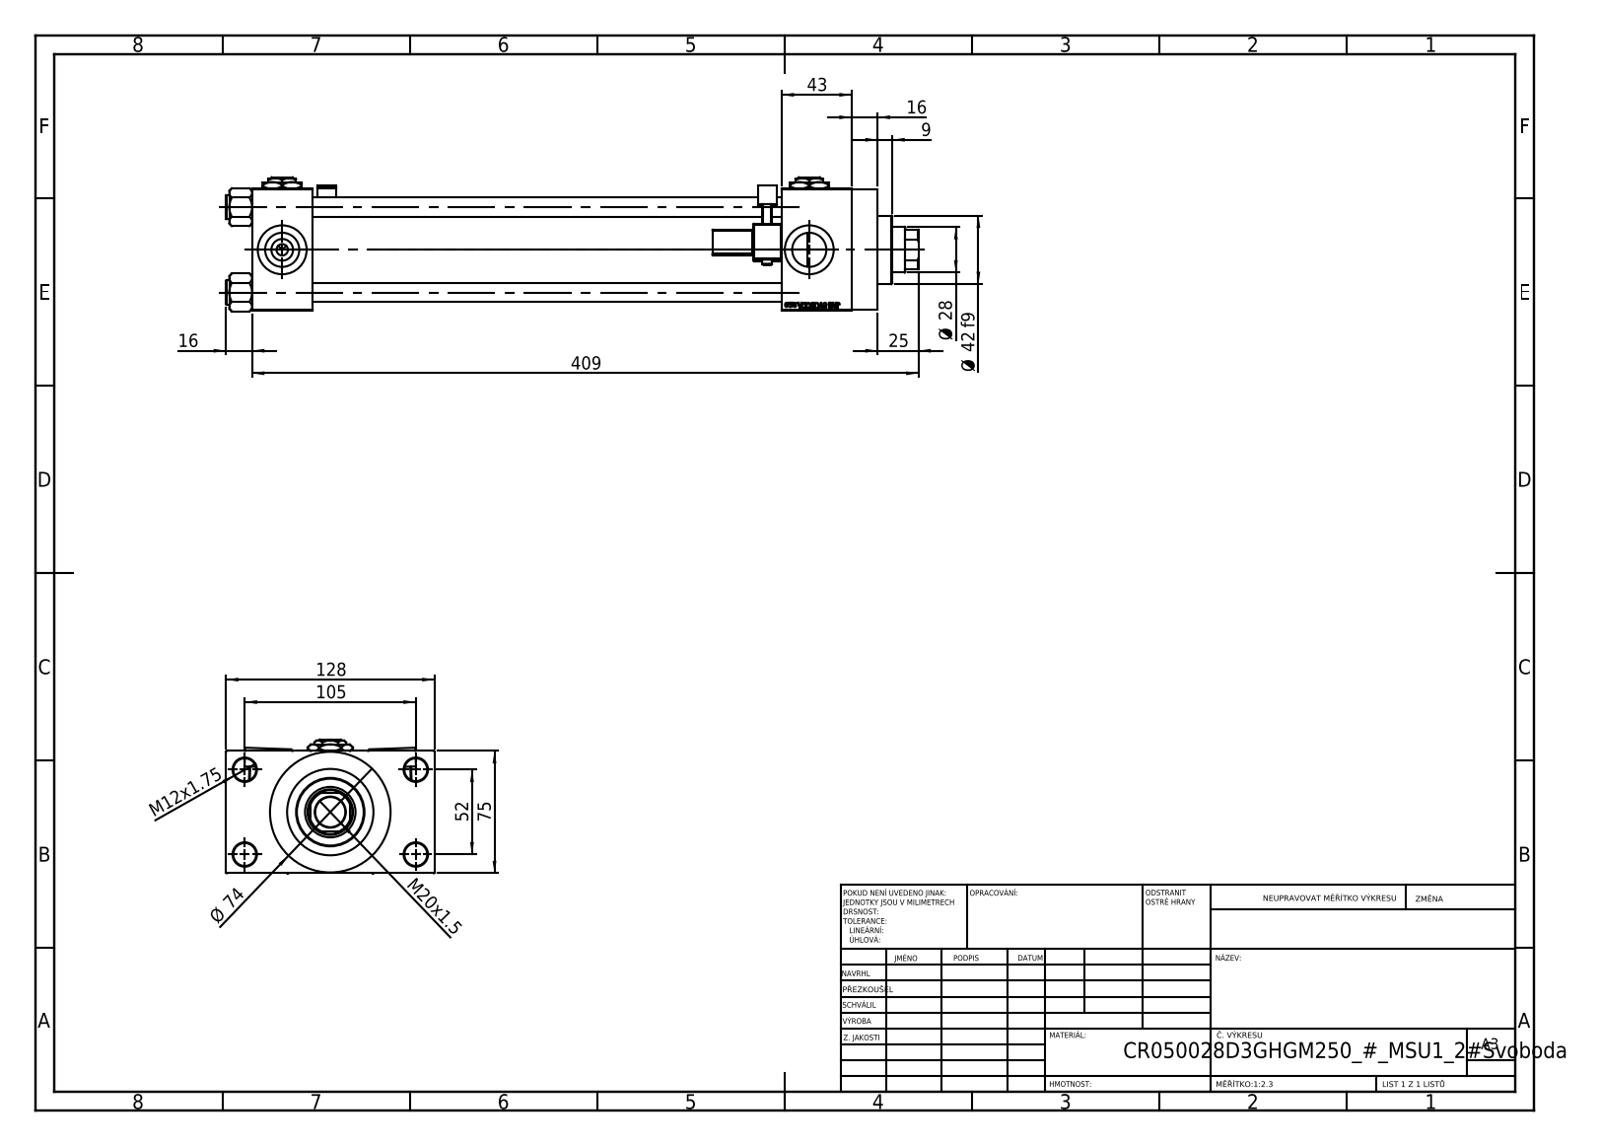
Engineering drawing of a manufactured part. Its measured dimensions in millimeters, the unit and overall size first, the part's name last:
Units: millimetres
Overall size (bounding box): 425 × 128 × 82.27
Round holes (diameter × count): ⌀12 ×4, ⌀14 ×4, ⌀20.96 ×4, ⌀30 ×4, ⌀7 ×3, ⌀18.5 ×1, ⌀28 ×1, ⌀31 ×1, ⌀41 ×1, ⌀50 ×1, ⌀53 ×1
Round bosses / shafts (diameter × count): ⌀15 ×4, ⌀6 ×2, ⌀74 ×1, ⌀56 ×1, ⌀42 ×1
Partial cylindrical surfaces — rounded edges, fillets, slot ends (radius × count): R0.5 ×48, R1 ×2, R2.5 ×2, R4 ×2, R13.5 ×1
Main face-to-face distances: 75, 288, 37, 325, 26.5, 101.5, 368, 331, 43, 16
Hole centre spacings: 26.35, 36.98, 52.3, 58.43, 58.59, 78.65, 94.37, 52
Volume: 1 204 000 mm³ · Surface area: 318 618 mm²
Bodies: 15 solids, 1358 faces (603 planar, 159 cylindrical, 596 other)
Part name (STEP PRODUCT): Zatka_pro_OIL_PORT; V215_VC_A; V215CR_D_TYCINKA; V215CR_VCP_D (+3 more)
STEP written by: SolidWorks 2019 (CONFIG_CONTROL_DESIGN)
